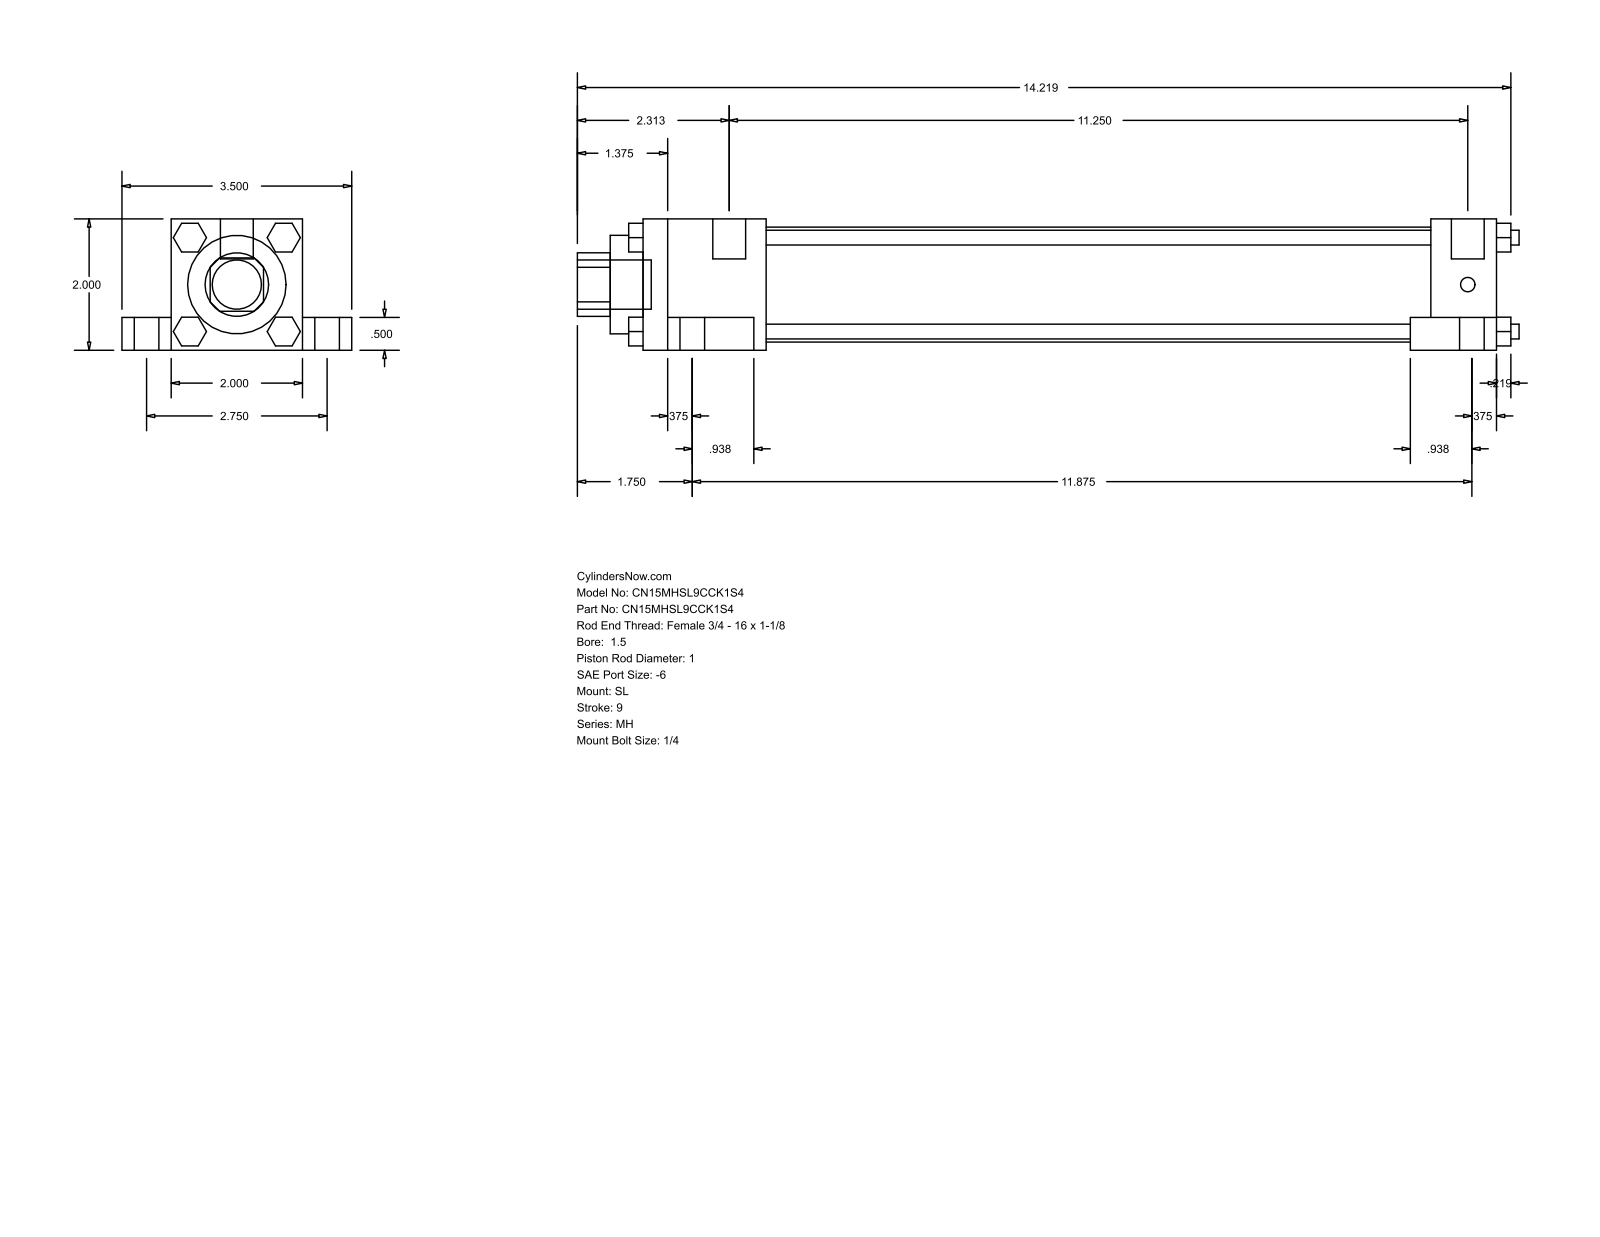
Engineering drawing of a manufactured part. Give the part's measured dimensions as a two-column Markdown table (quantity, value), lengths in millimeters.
| quantity | value |
| --- | --- |
| part name | MH_SL__0150_1 |
| STEP written by | GSSL Pune (CONFIG_CONTROL_DESIGN) |
| units | millimeters |
| bodies | 0 solids, 148 faces (112 planar, 36 cylindrical, 0 other) |
| overall size | 364.33 × 88.9 × 50.8 |
| round holes (diameter × count) | 25.4 × 1, 38.1 × 1, 44.45 × 1 |
| round bosses / shafts (diameter × count) | 15.88 × 4, 9.53 × 4, 5.71 × 4, 5.56 × 4, 12.7 × 2, 19.05 × 1 |
| partial cylindrical surfaces (radius × count) | 12.29 × 1 |
| main face-to-face distances | 50.8, 12.7, 38.1, 19.05, 69.85, 330.2, 25.4, 9.52, 33.34, 287.34 |
